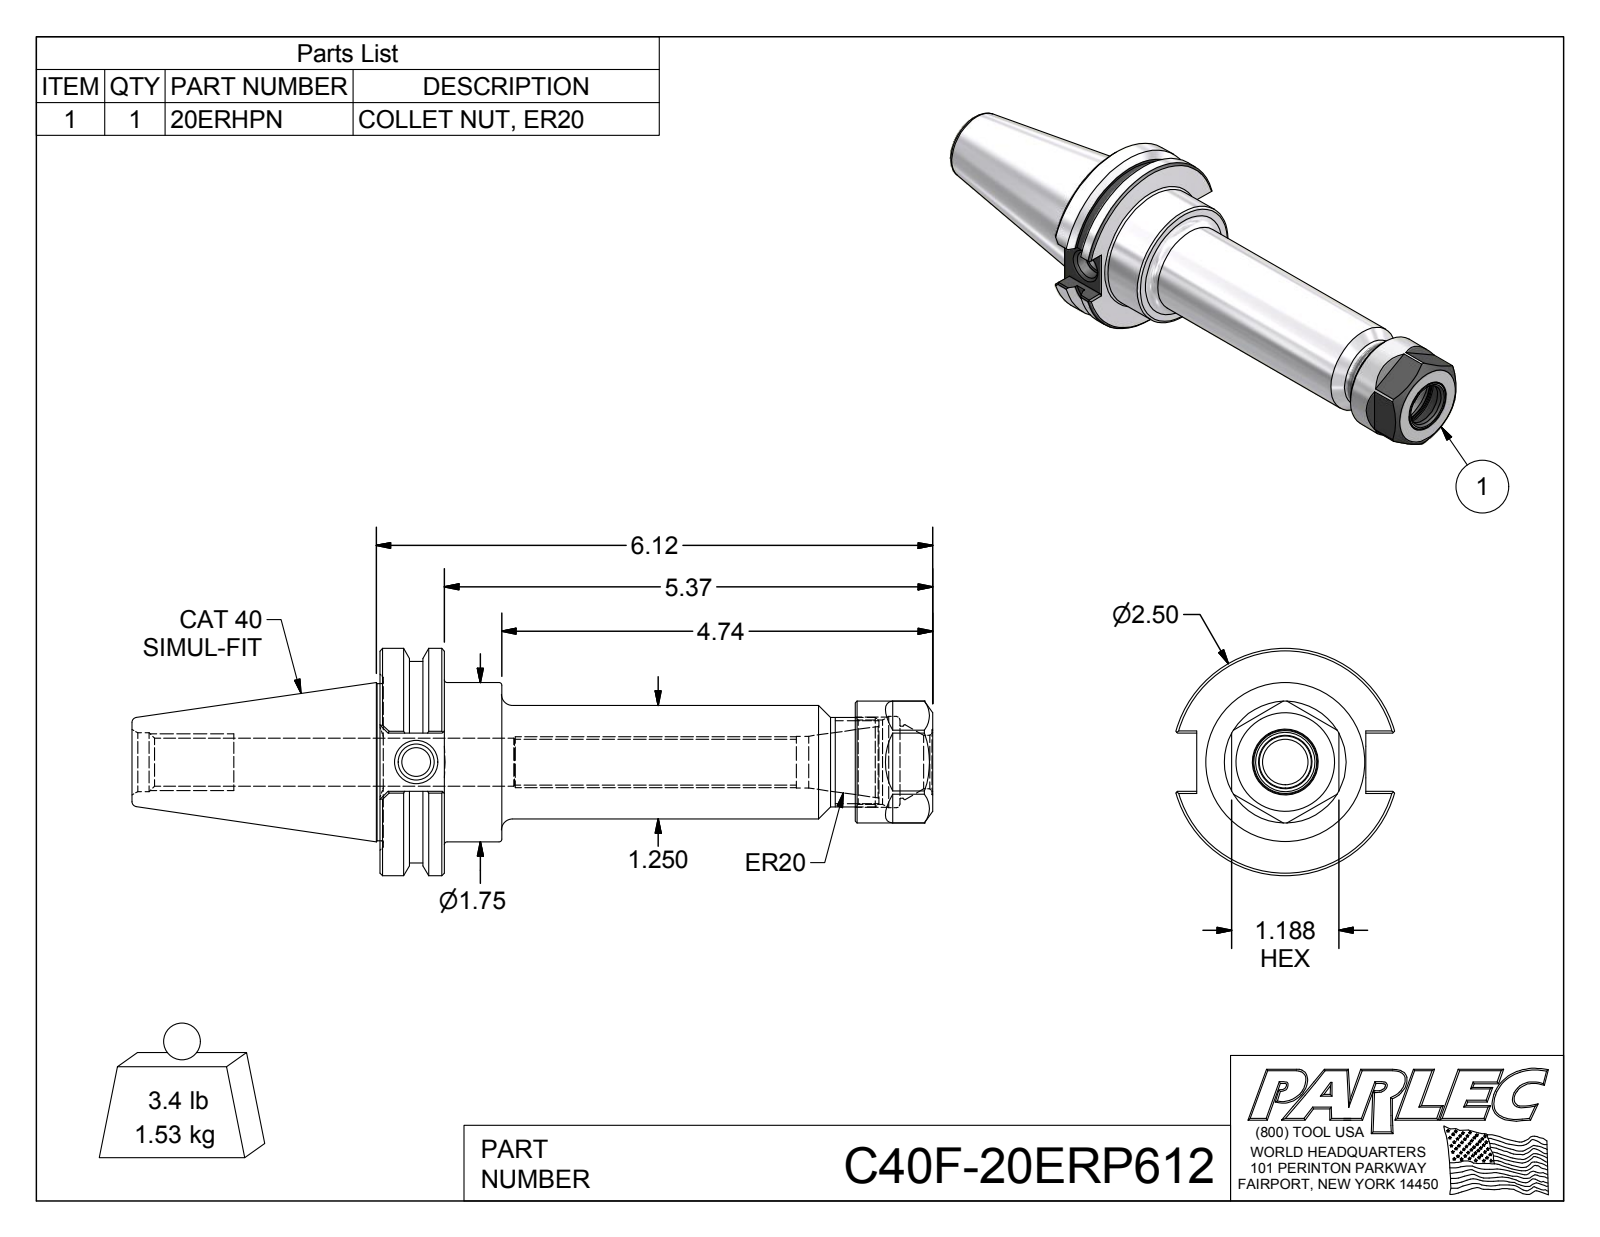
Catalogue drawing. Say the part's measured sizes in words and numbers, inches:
The part is named "C40F-20ERP612; C40F-20ER6-1; 20ERHPN". Its 3-D file was written by "Autodesk Inventor 2012 (AUTOMOTIVE_DESIGN)". It is 2 solids with 112 faces: 50 planar, 21 cylindrical and 41 other. Overall it measures 8.808 by 2.5 by 2.406 inches. Its volume is 12.13 cubic inches and its surface area 65.9 square inches. Round holes: 1 of diameter 0.315, 1 of diameter 0.399, 1 of diameter 0.502, 1 of diameter 0.527, 1 of diameter 0.57, 1 of diameter 0.587, 1 of diameter 0.648, 1 of diameter 0.79, 1 of diameter 0.926, 1 of diameter 1.005. Round bosses or shafts: 1 of diameter 2.5, 1 of diameter 2.215, 1 of diameter 1.75, 1 of diameter 1.73, 1 of diameter 1.34, 1 of diameter 1.25, 1 of diameter 0.984. The main face-to-face distances are 0.71, 1.18, 5.23, 4.52, 6.08, 5.37, 0.85, 1.34, 0.63, 3.89.
